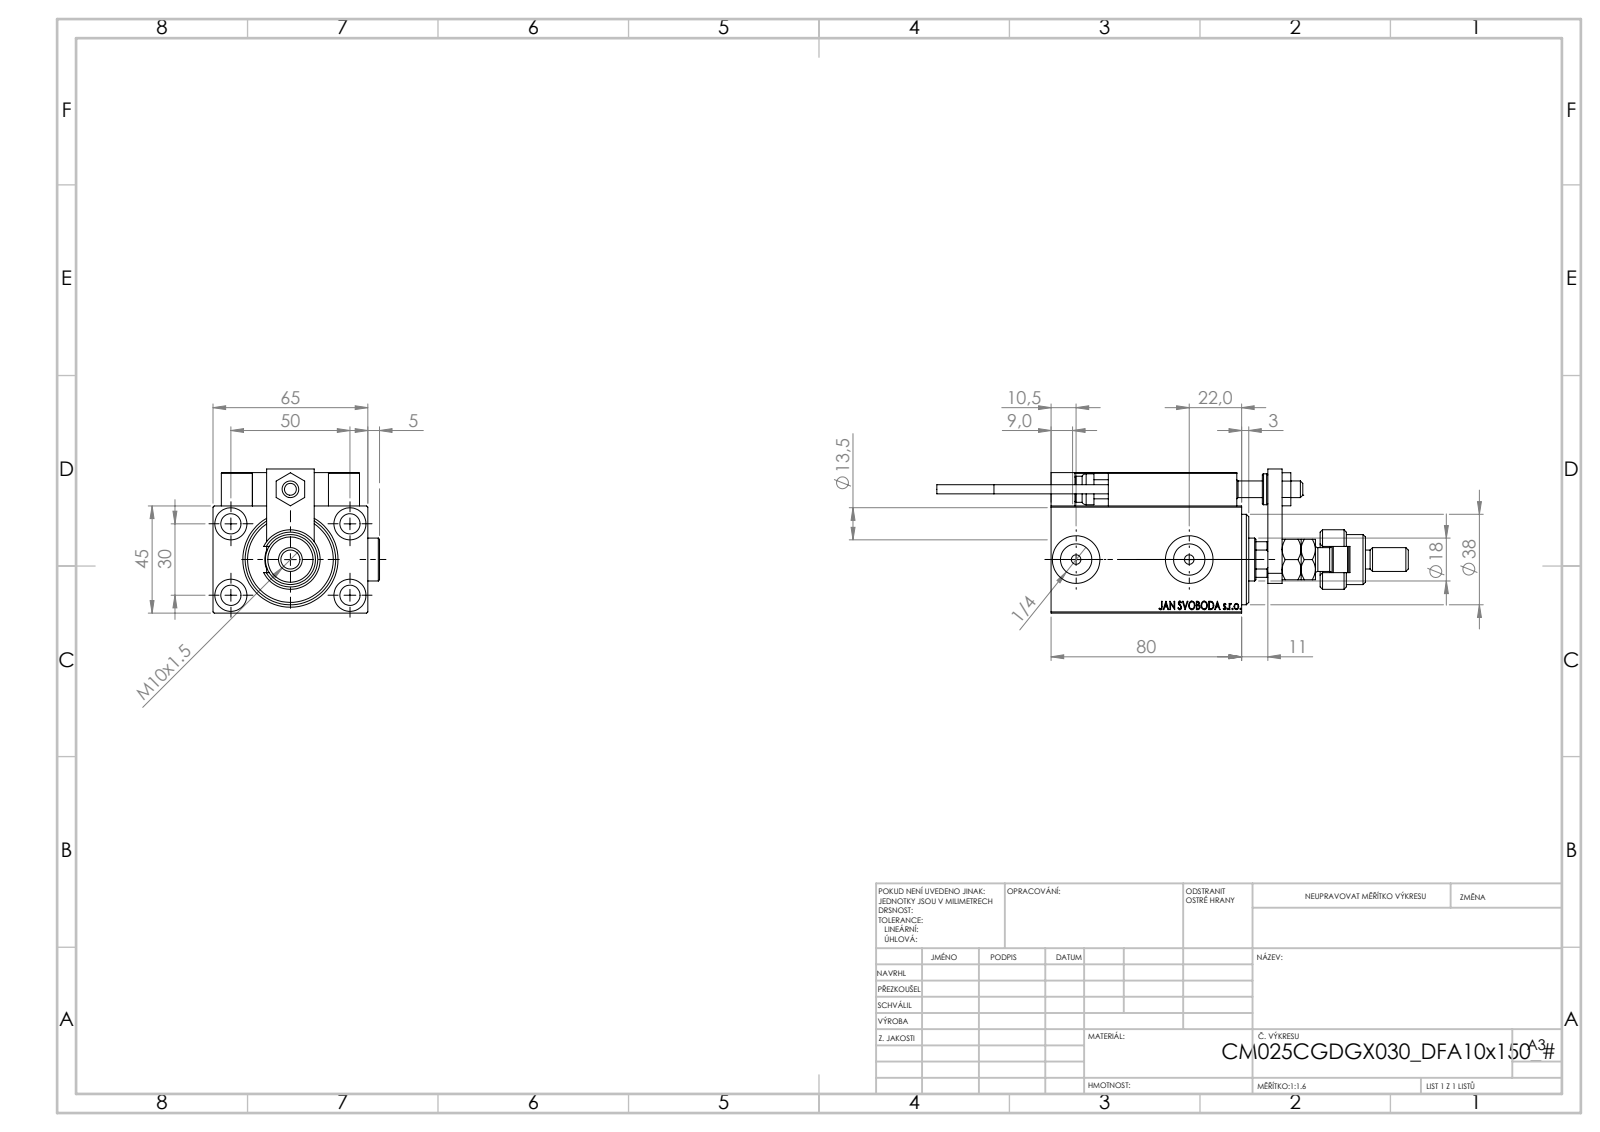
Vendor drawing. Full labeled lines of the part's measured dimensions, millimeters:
Part name (STEP PRODUCT): FEMALE_PART_FOR_DFA; V450CM_VC_B; KONCOVKA; SWITCH_X_FRONT_BACK (+7 more)
STEP written by: SolidWorks 2019 (CONFIG_CONTROL_DESIGN)
Units: millimetres
Bodies: 27 solids, 1421 faces (622 planar, 217 cylindrical, 582 other)
Overall size (bounding box): 198 × 69.9 × 60.5
Volume: 258 544 mm³ · Surface area: 82 379 mm²
Round holes (diameter × count): ⌀4 ×6, ⌀8 ×5, ⌀8.5 ×5, ⌀3.2 ×4, ⌀13.5 ×4, ⌀5 ×2, ⌀13.16 ×2, ⌀20 ×2, ⌀7 ×1, ⌀14.5 ×1, ⌀18 ×1, ⌀21.5 ×1
Round bosses / shafts (diameter × count): ⌀18 ×2, ⌀5 ×2, ⌀3.8 ×2, ⌀25 ×1, ⌀21 ×1, ⌀16 ×1, ⌀13 ×1, ⌀11 ×1
Partial cylindrical surfaces — rounded edges, fillets, slot ends (radius × count): R0.3 ×30, R3 ×2, R5.5 ×1, R8.5 ×1, R8.75 ×1
Main face-to-face distances: 45, 14, 65, 59, 6, 3, 5, 13, 7, 91
Hole centre spacings: 29.15, 11.37, 20, 28.9, 29.59, 29.69, 30, 32.06
